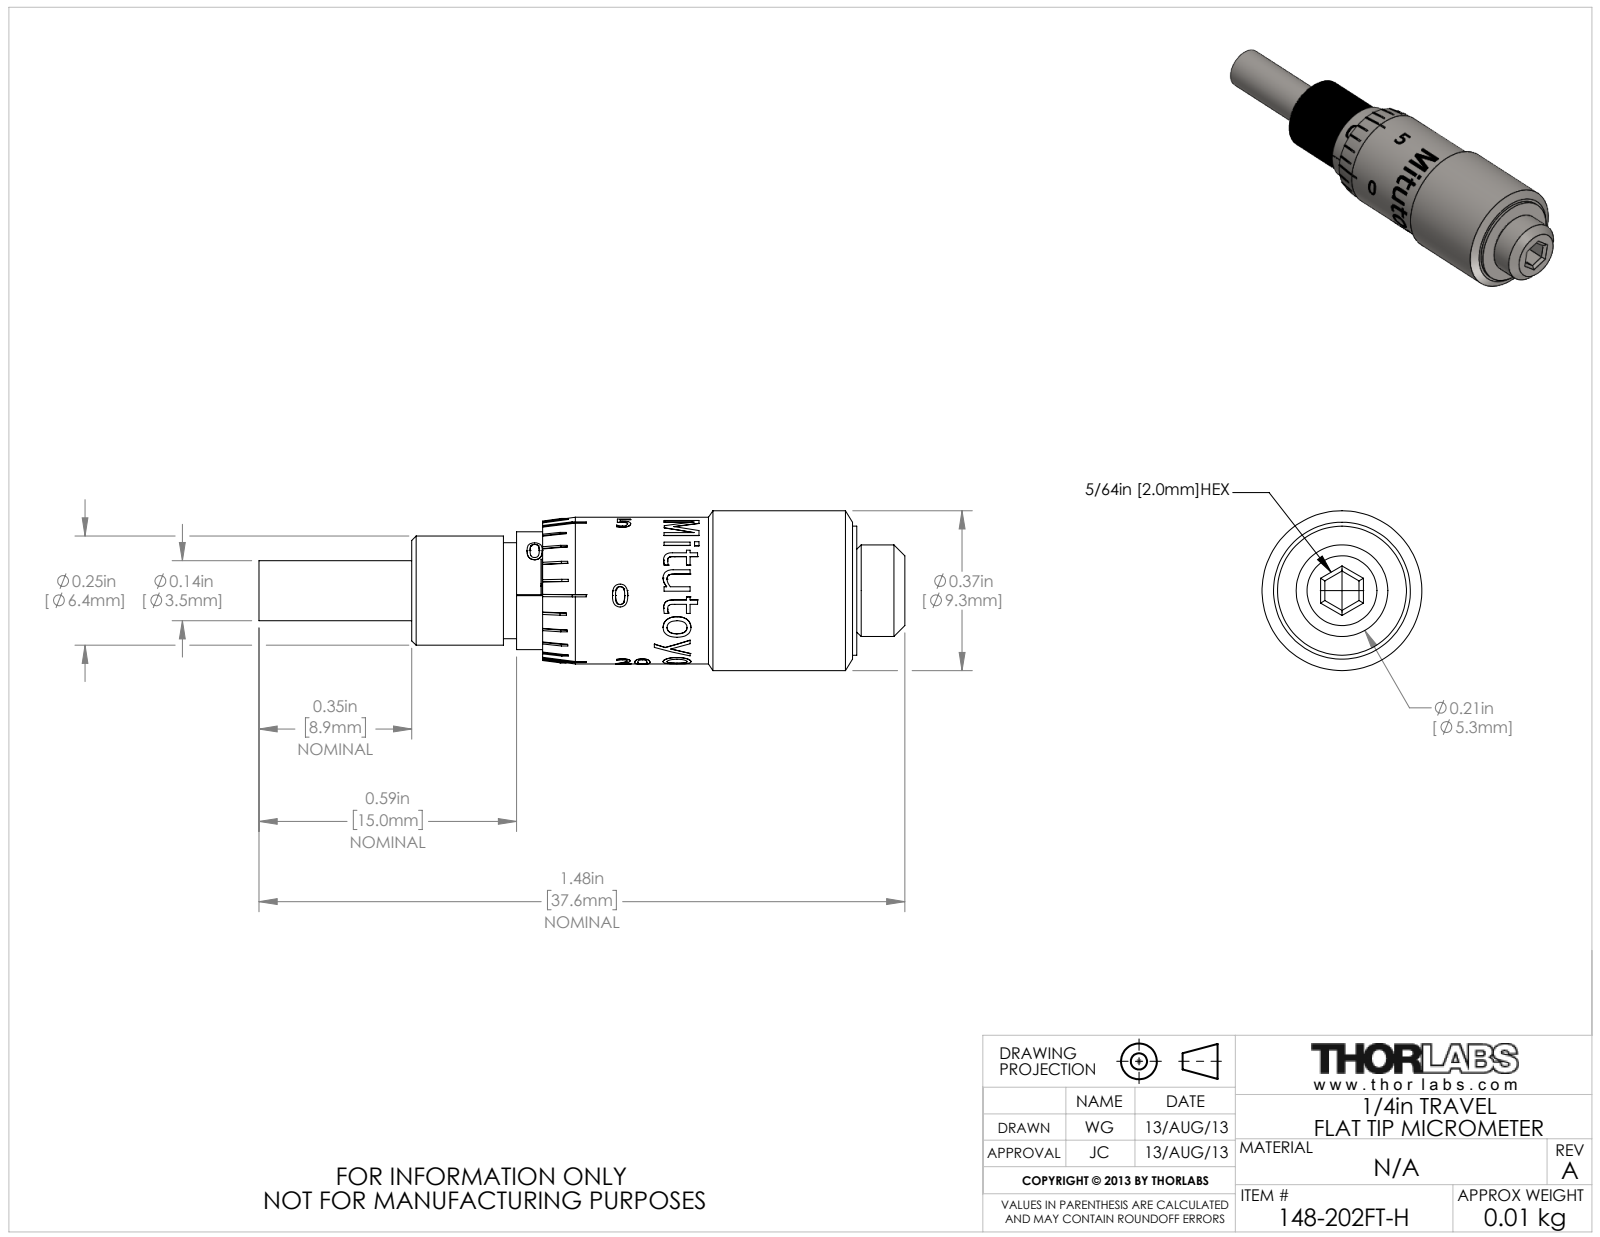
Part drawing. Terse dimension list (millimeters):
name: TTN017219-E0W
written by: SolidWorks 2012 (AUTOMOTIVE_DESIGN)
unit: mm
bodies: 2 solids, 424 faces (184 planar, 72 cylindrical, 168 other)
size: 37.6 × 9.3 × 9.3
volume: 1 500 mm³; area: 1 067 mm²
holes: 1× ⌀2.3
bosses: 1× ⌀9.3, 1× ⌀8.5, 1× ⌀7.5, 1× ⌀6.9, 1× ⌀6.4, 1× ⌀5.6, 1× ⌀5.3, 1× ⌀3.5
rounds: 5× R4.2, 5× R4.3, 1× R3.4, 1× R4.3
face distances: 25.9, 7.6, 18.3, 6.1, 1.5, 19.8, 15, 16.5, 8.9, 34.8
